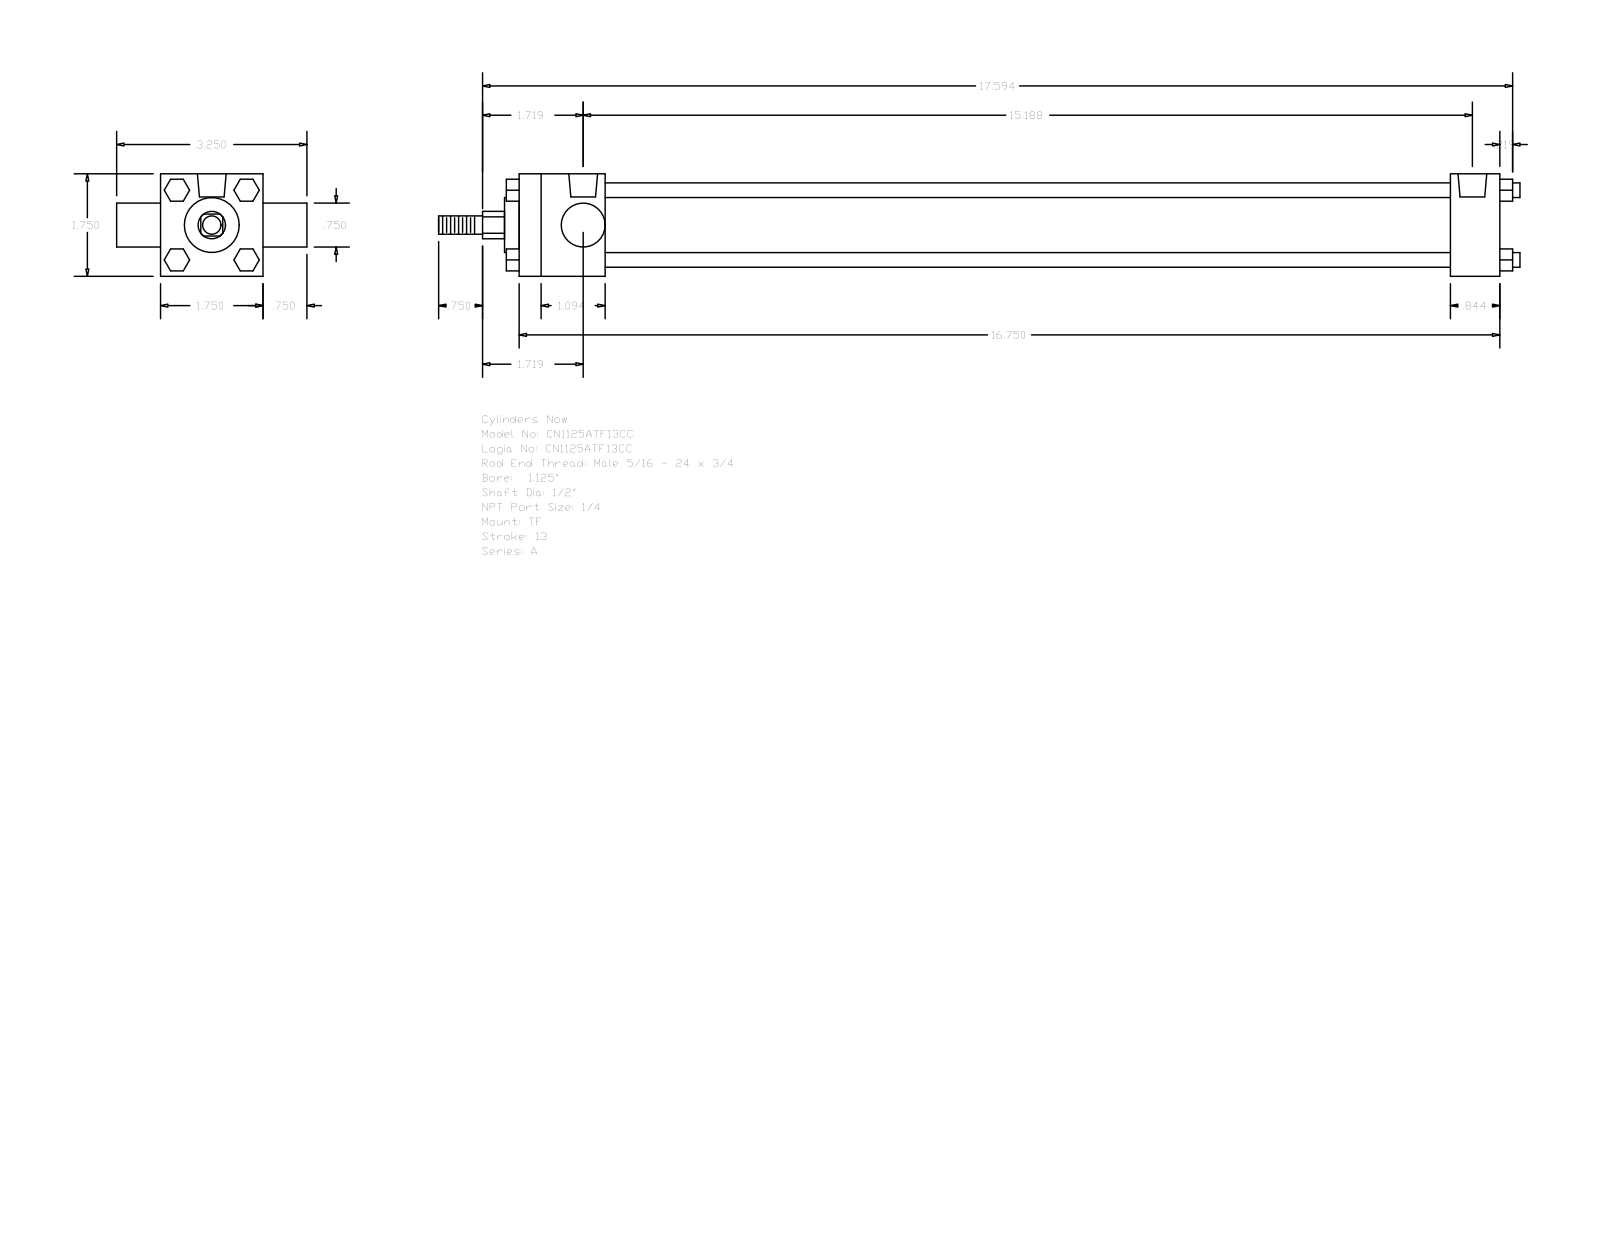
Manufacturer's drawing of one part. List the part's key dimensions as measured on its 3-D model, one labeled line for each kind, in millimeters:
Part name (STEP PRODUCT): A_TF__0112_0.5
STEP written by: GSSL Pune (CONFIG_CONTROL_DESIGN)
Units: millimetres
Bodies: 0 solids, 120 faces (92 planar, 28 cylindrical, 0 other)
Overall size (bounding box): 469.11 × 82.55 × 44.45
Round holes (diameter × count): ⌀5.56 ×3, ⌀12.49 ×2
Round bosses / shafts (diameter × count): ⌀6.35 ×4, ⌀31.88 ×1, ⌀23.81 ×1, ⌀19.05 ×1, ⌀12.7 ×1, ⌀7.94 ×1
Partial cylindrical surfaces — rounded edges, fillets, slot ends (radius × count): R5.94 ×1
Main face-to-face distances: 44.46, 425.44, 404.01, 21.43, 37.3, 366.71, 388.14, 19.04, 63.5, 9.53
Hole centre spacings: 1.58, 1.59, 382.59, 384.17, 384.18, 385.76
